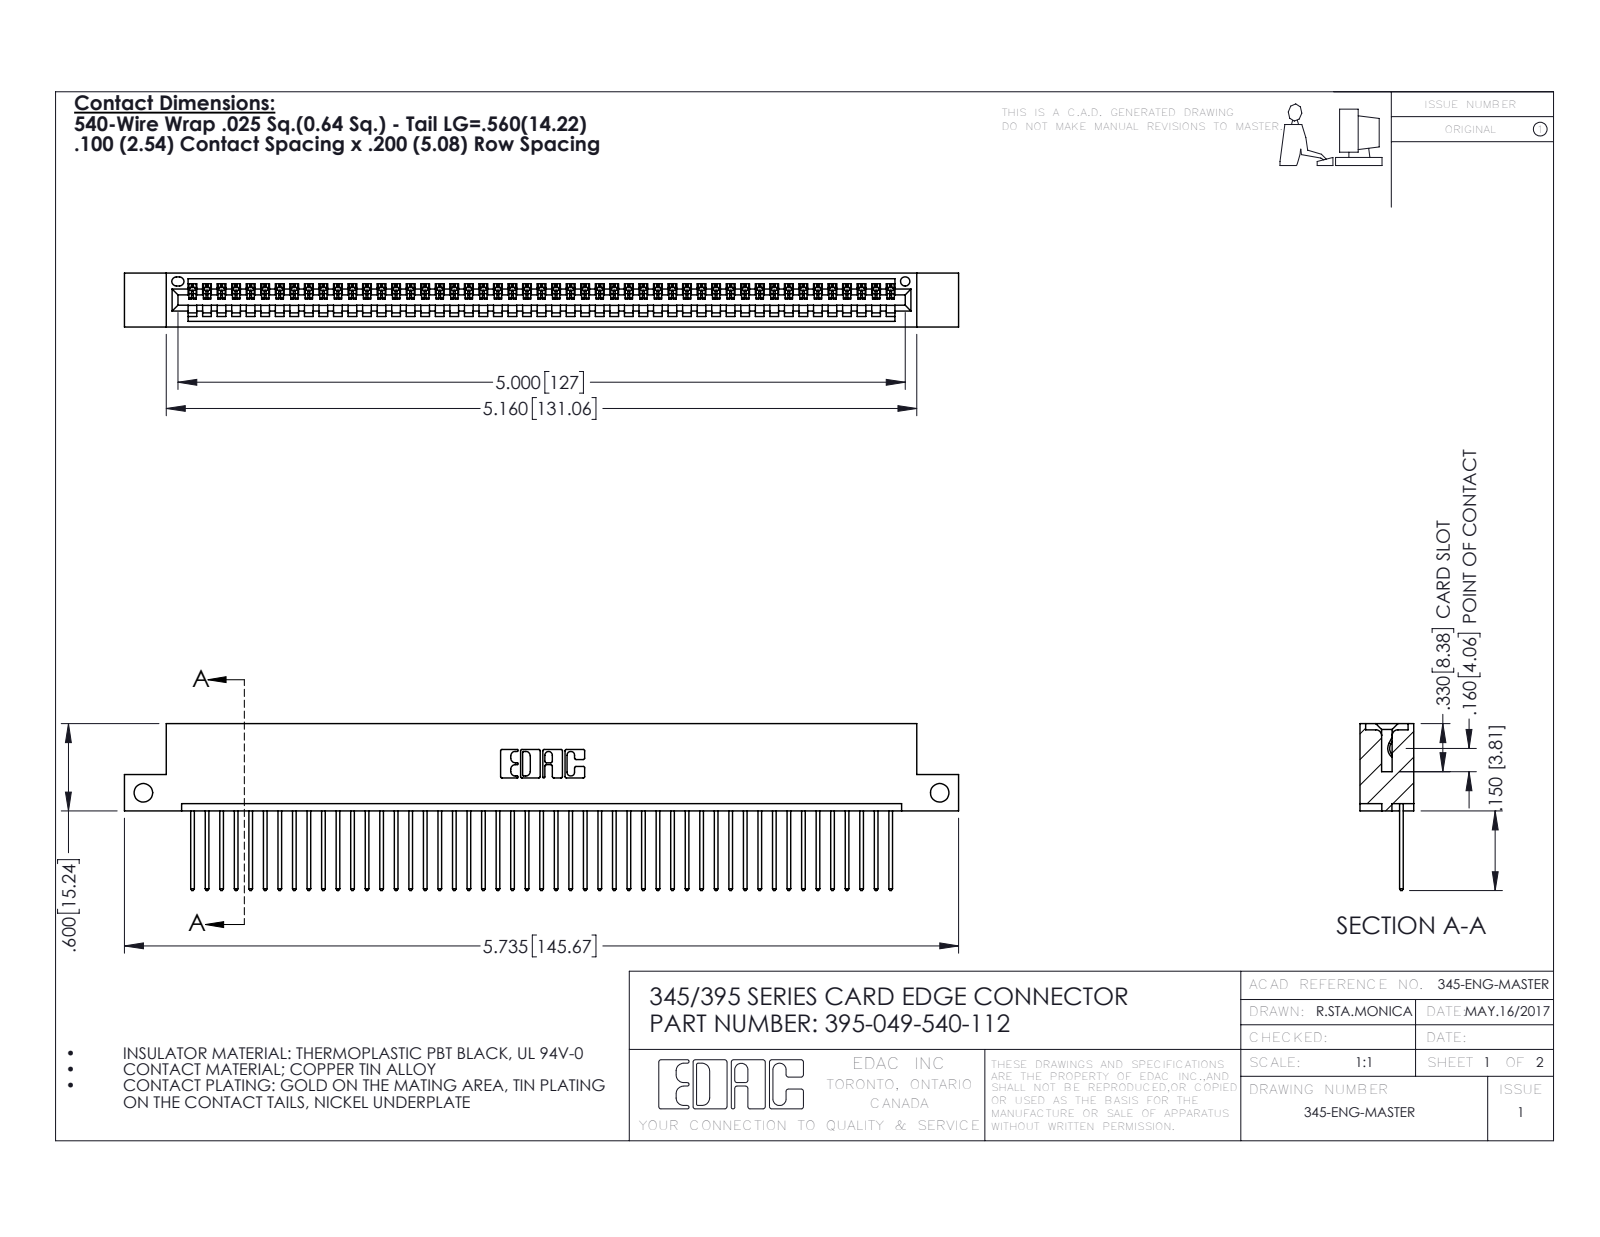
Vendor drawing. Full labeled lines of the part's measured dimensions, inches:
Part name (STEP PRODUCT): 345 Part_Flush Mounting Lugs - Side Mount; 345-292-001_345-293-140; 395-049-540-112
STEP written by: SolidWorks 2016 (CONFIG_CONTROL_DESIGN)
Units: inches
Bodies: 50 solids, 2968 faces (2040 planar, 928 cylindrical, 0 other)
Overall size (bounding box): 5.735 × 1.147 × 0.37
Volume: 0.847 in³ · Surface area: 29.24 in²
Round holes (diameter × count): ⌀0.128 ×2, ⌀0.064 ×1
Partial cylindrical surfaces — rounded edges, fillets, slot ends (radius × count): R0.006 ×98, R0.01 ×98, R0.01 ×22, R0.007 ×6, R0.031 ×6, R0.026 ×3, R0.031 ×2, R0.04 ×2
Main face-to-face distances: 0.298, 0.072, 0.2, 0.37, 0.098, 0.272, 0.025, 0.225, 0.149, 0.072
Hole centre spacings: 5.475
